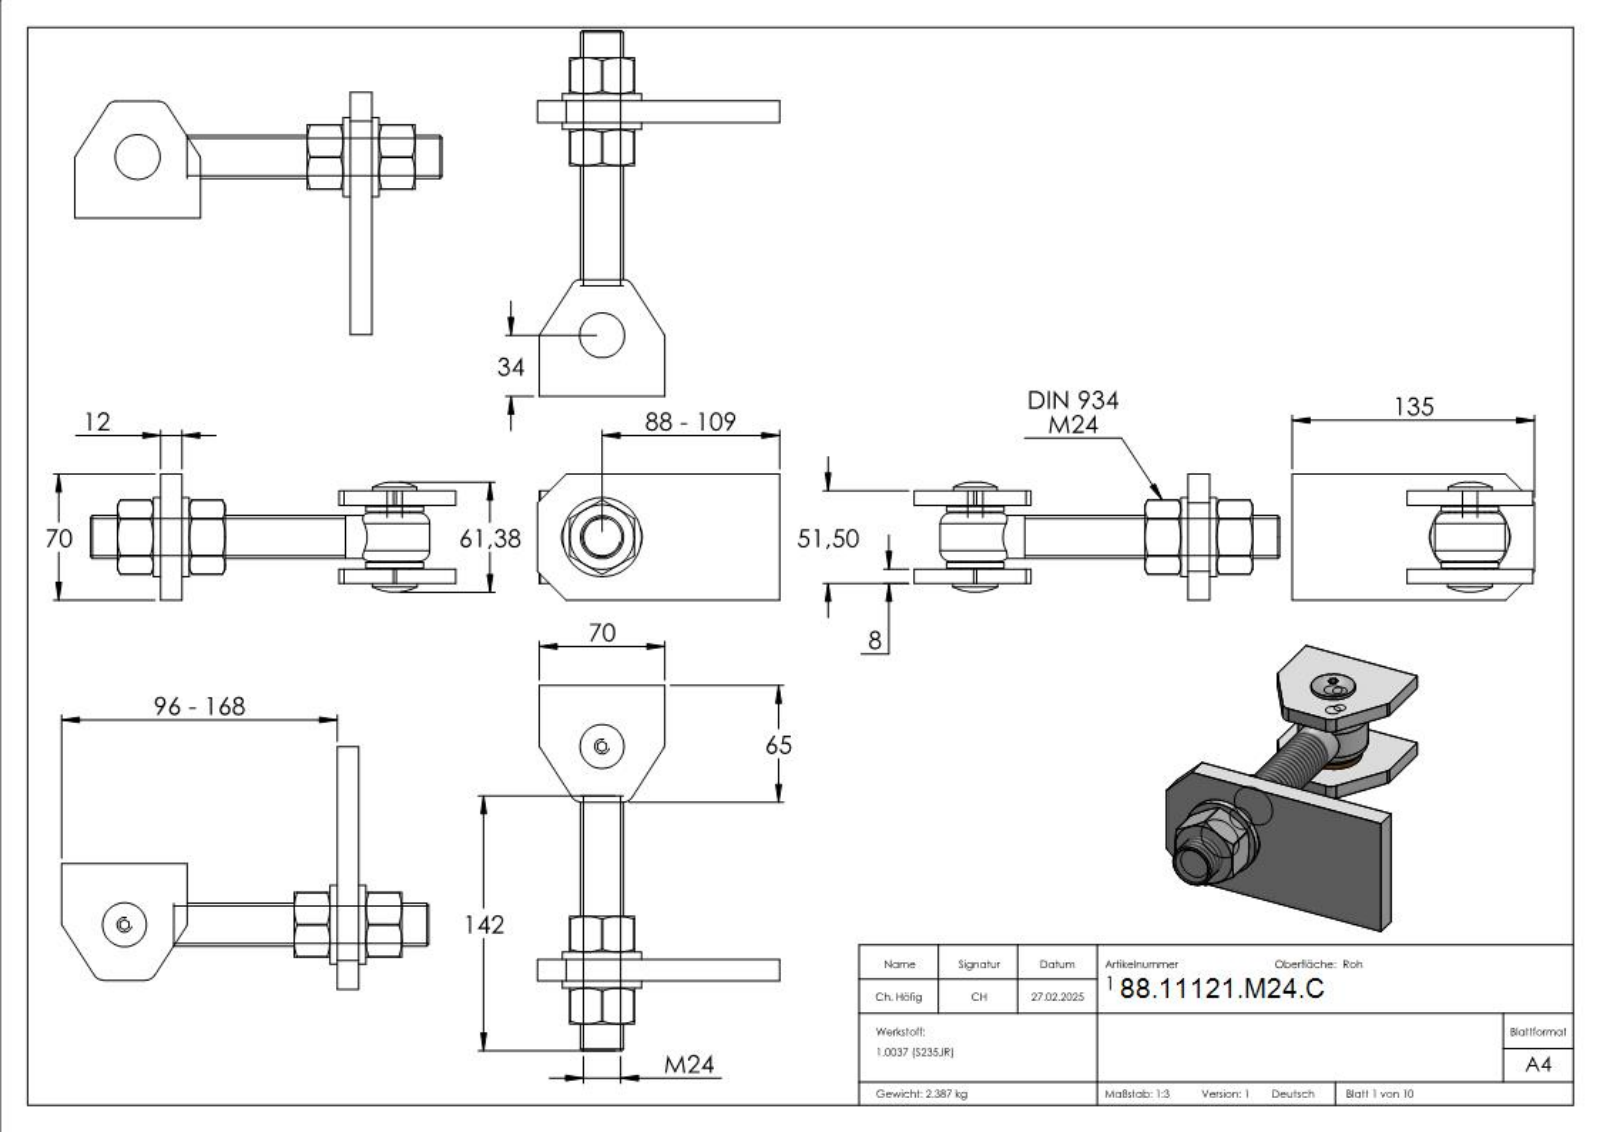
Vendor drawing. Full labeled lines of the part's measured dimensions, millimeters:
Part name (STEP PRODUCT): Torband Teil5_121-M24-GV Teil5; Torband Teil1_121-M24-GV Teil1A; Torband Teil1_121-M24-GV Teil1B; 121-Mxx Teil6_121-M24-GV Teil6 (+6 more)
STEP written by: SolidWorks 2018 (CONFIG_CONTROL_DESIGN)
Units: millimetres
Bodies: 12 solids, 600 faces (407 planar, 41 cylindrical, 152 other)
Overall size (bounding box): 200.75 × 180 × 70
Volume: 338 251 mm³ · Surface area: 93 838 mm²
Round holes (diameter × count): ⌀8.5 ×1, ⌀20.5 ×1, ⌀20.6 ×1, ⌀21 ×1, ⌀26 ×1
Round bosses / shafts (diameter × count): ⌀44 ×1, ⌀40 ×1, ⌀27 ×1, ⌀25 ×1, ⌀24 ×1, ⌀19.7 ×1, ⌀10 ×1
Partial cylindrical surfaces — rounded edges, fillets, slot ends (radius × count): R0.5 ×6, R3 ×3, R10 ×2, R13 ×2
Main face-to-face distances: 12, 36, 8, 13, 28, 44, 21, 49, 57, 15.5
